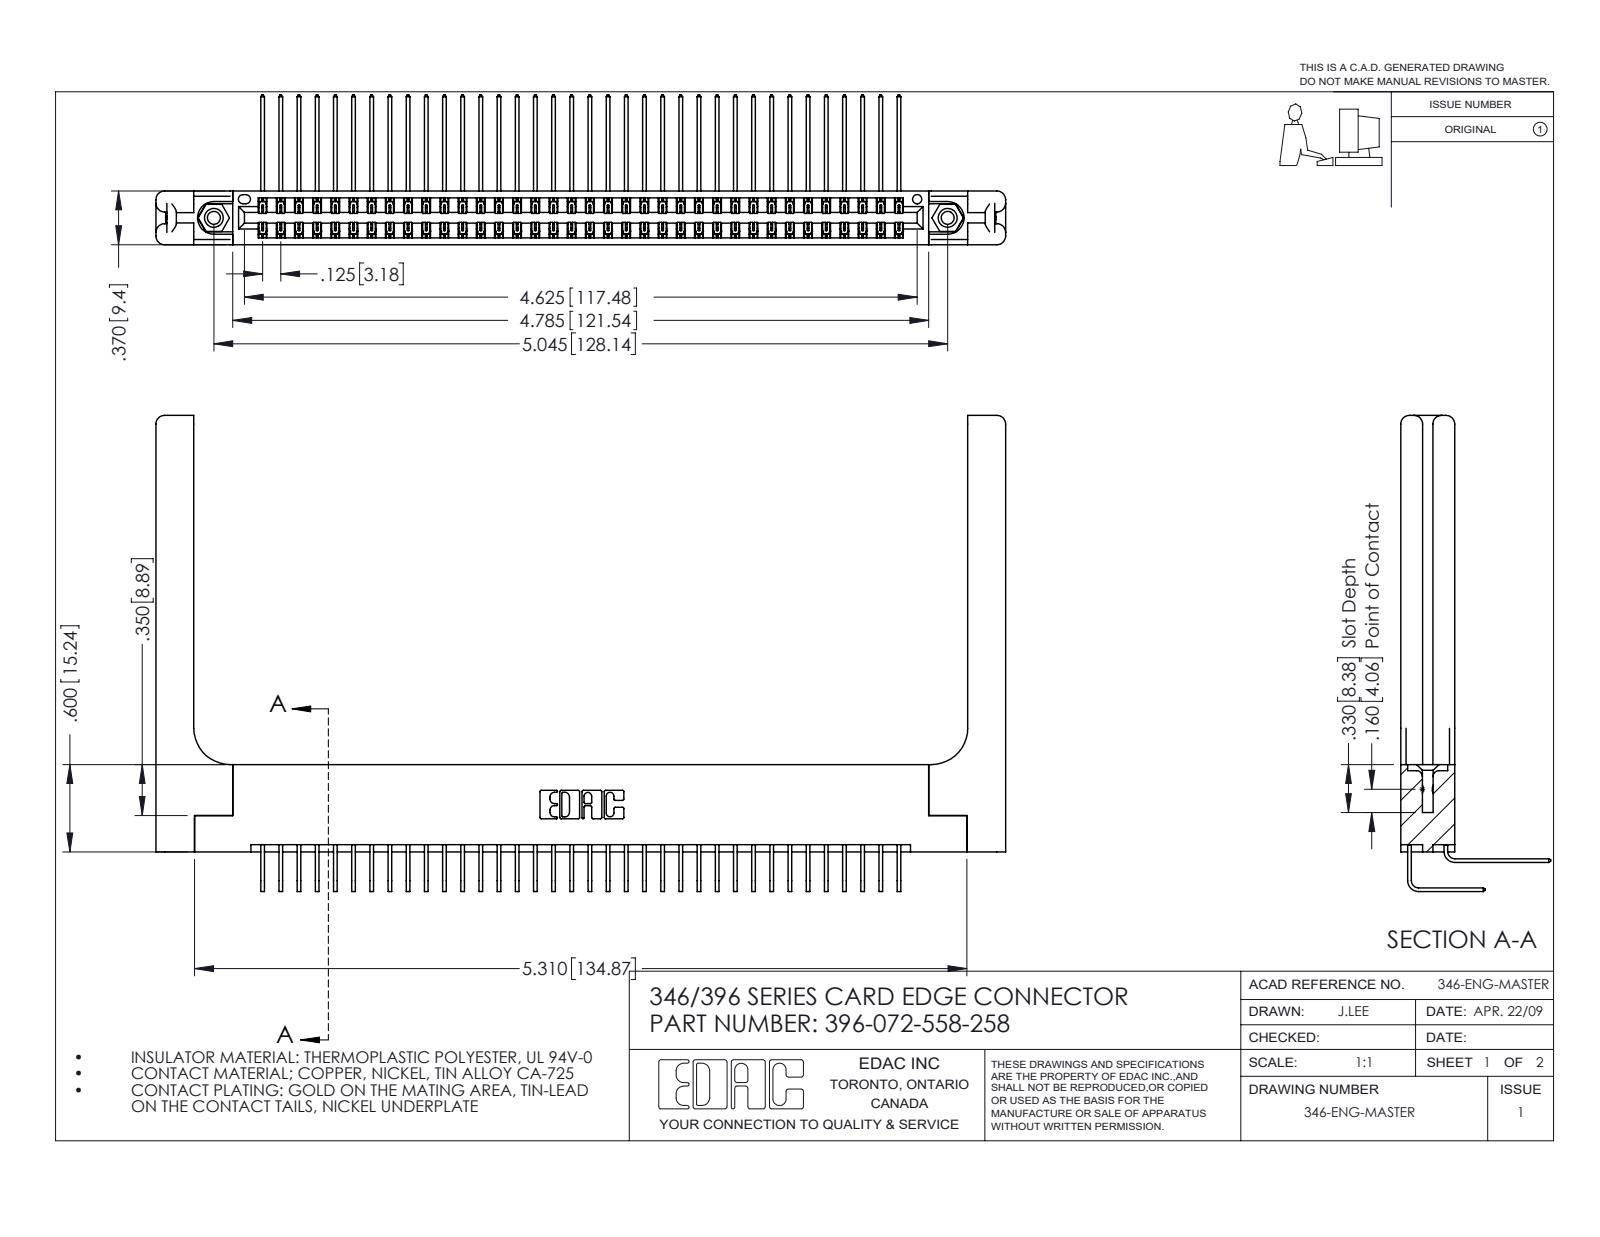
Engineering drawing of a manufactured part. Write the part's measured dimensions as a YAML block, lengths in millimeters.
part_name: "396-072-558-258; 345-292-001_558 Tail - 2; 345-250-001_345-250-001-102; 346-220-058_345-220-058 (+2 more)"
step_written_by: "SolidWorks 2016 (CONFIG_CONTROL_DESIGN)"
units: millimeters
bodies: {solids: 77, faces: 4266, planar: 2888, cylindrical: 1318, other: 60}
overall_size: [148.4, 83.1, 26.2]
volume: 22340
surface_area: 27260
round_holes:
  - {diameter: 2.3, count: 2}
  - {diameter: 3.2, count: 2}
  - {diameter: 4, count: 2}
  - {diameter: 1.6, count: 1}
round_bosses_or_shafts:
  - {diameter: 3.9, count: 2}
partial_cylinders:
  - {radius: 0.2, count: 108}
  - {radius: 0.3, count: 22}
  - {radius: 1.5, count: 16}
  - {radius: 0.2, count: 6}
  - {radius: 0.8, count: 6}
  - {radius: 0.7, count: 3}
  - {radius: 0.4, count: 2}
  - {radius: 0.6, count: 2}
face_to_face_distances: [8.2, 1.2, 9.4, 1.8, 0.6, 7.6, 3.8, 3.8, 6.4, 7]
hole_center_spacings: [6.2, 122.8, 128.1]
